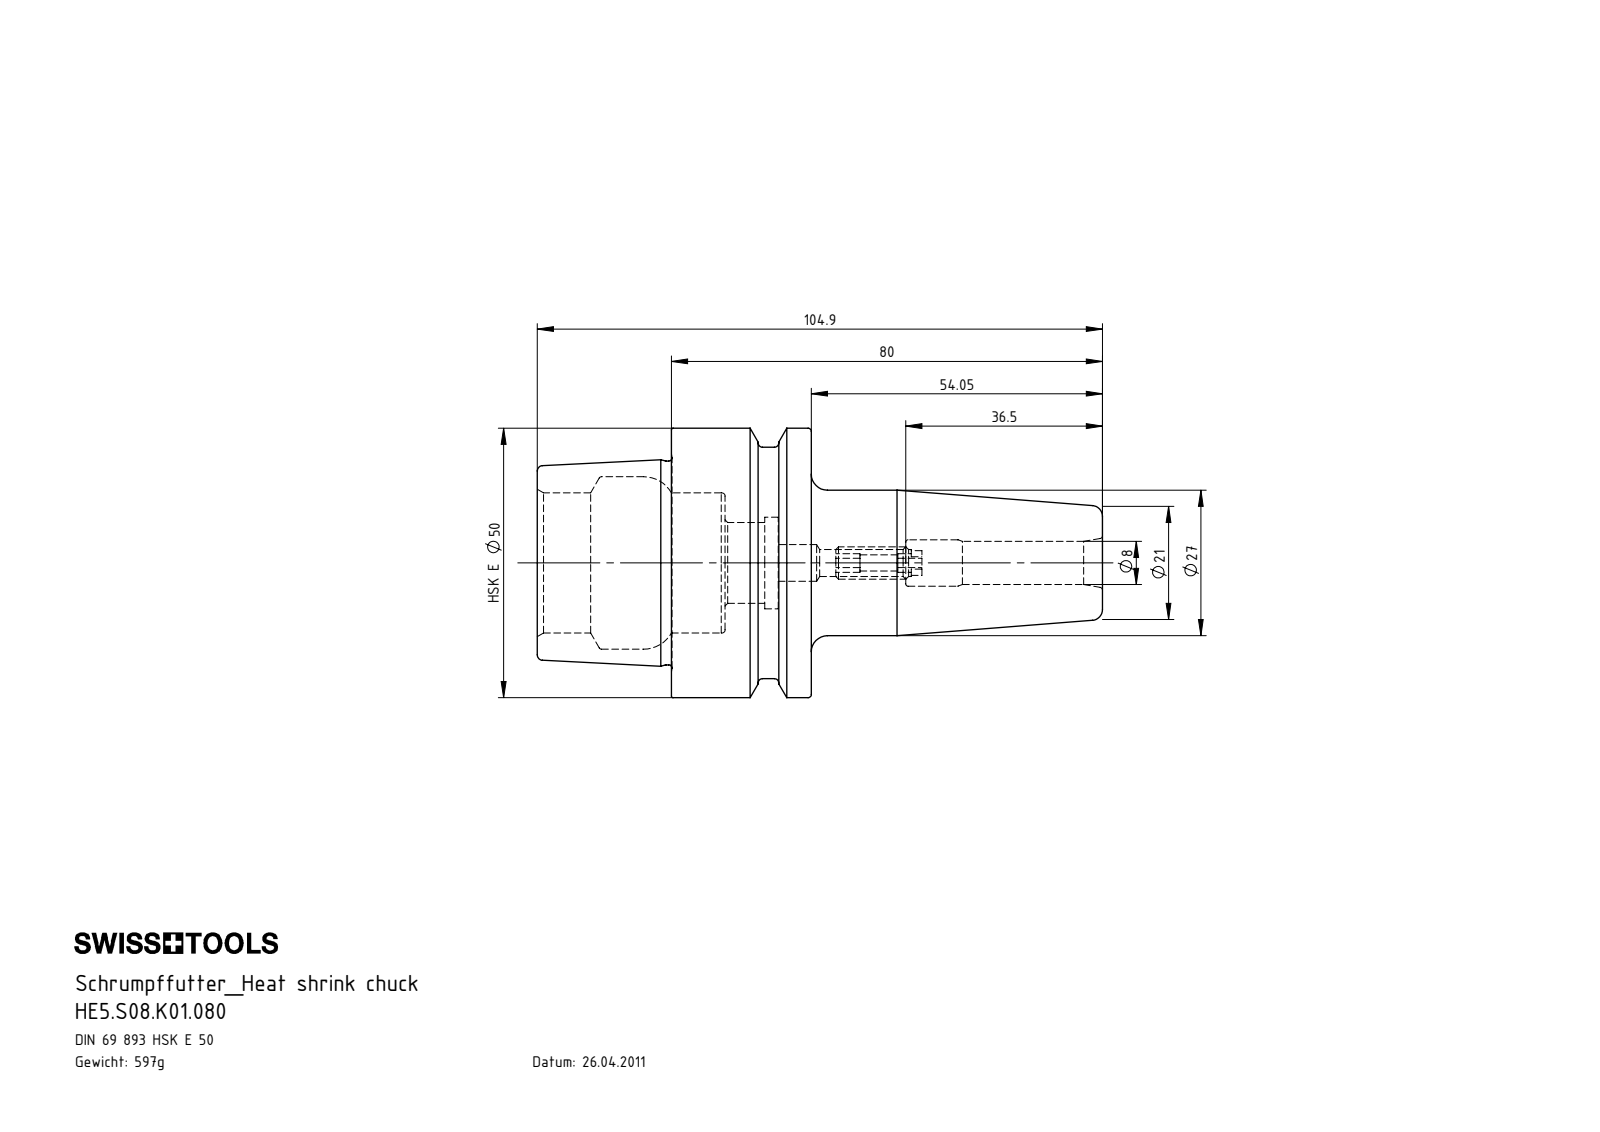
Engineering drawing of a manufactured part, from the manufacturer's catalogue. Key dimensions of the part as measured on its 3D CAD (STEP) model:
Part name (STEP PRODUCT): ERU-AN2.K01.016_A; HE5-S08.K01.080_B_Fertigbearbeitung; HE5.S08.K01.080
STEP written by: SolidWorks 2017 (AUTOMOTIVE_DESIGN)
Units: millimetres
Bodies: 2 solids, 142 faces (43 planar, 34 cylindrical, 65 other)
Overall size (bounding box): 104.9 × 50 × 50
Volume: 76 038 mm³ · Surface area: 20 661 mm²
Round holes (diameter × count): ⌀3 ×1, ⌀5 ×1, ⌀6.8 ×1, ⌀8 ×1, ⌀8.6 ×1, ⌀15 ×1, ⌀17 ×1, ⌀26 ×1, ⌀32 ×1
Round bosses / shafts (diameter × count): ⌀50 ×1, ⌀42.95 ×1, ⌀37.81 ×1, ⌀27 ×1, ⌀6 ×1
Main face-to-face distances: 25.95, 24.9, 50.85, 16, 34.85, 9.95, 44.7, 19.8, 9.85, 6.15
